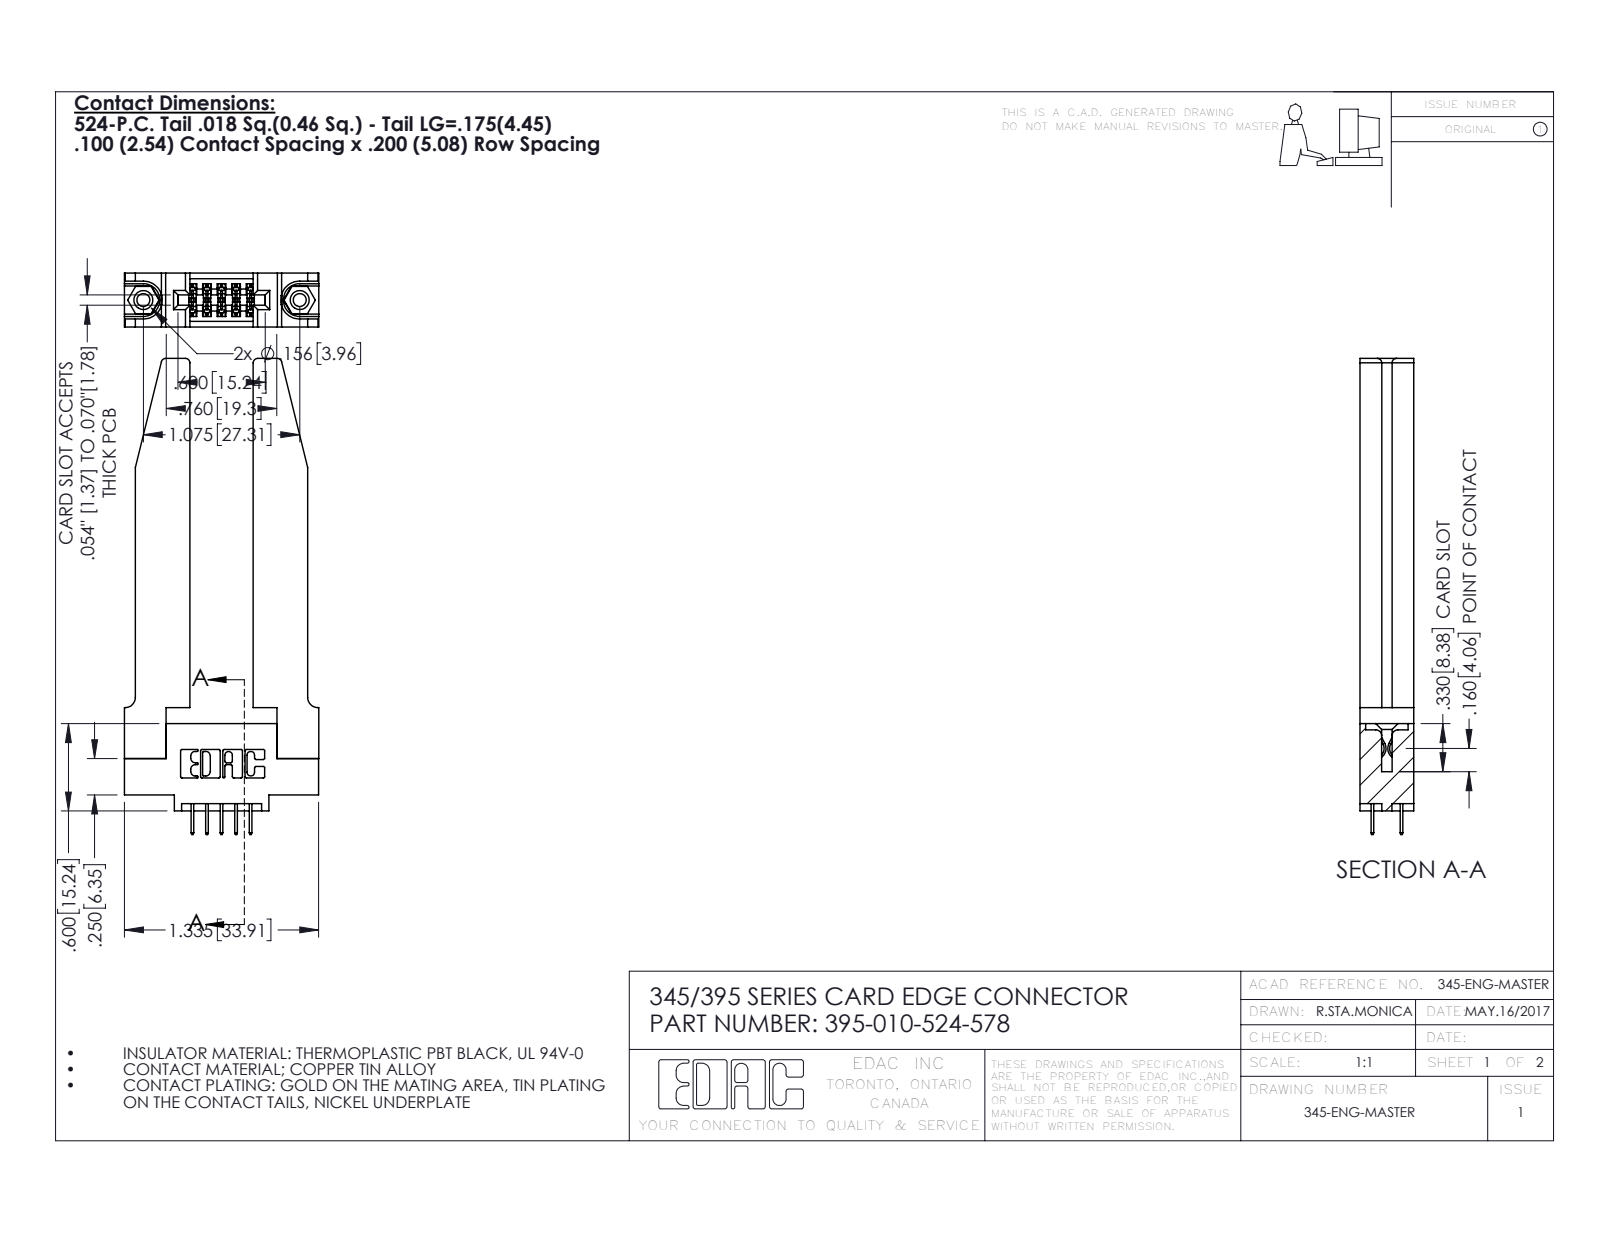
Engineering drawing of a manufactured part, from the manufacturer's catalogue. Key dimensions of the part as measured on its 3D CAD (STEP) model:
Part name (STEP PRODUCT): 345-292-001_345-293-124; 345-250-001_345-250-001-102; 345-220-078_345-220-078; 345 Part_0.110 Offset - 0.156 Dia-TH (+1 more)
STEP written by: SolidWorks 2016 (CONFIG_CONTROL_DESIGN)
Units: inches
Bodies: 15 solids, 904 faces (616 planar, 236 cylindrical, 52 other)
Overall size (bounding box): 3.272 × 1.336 × 0.37
Volume: 0.649 in³ · Surface area: 16.13 in²
Round holes (diameter × count): ⌀0.089 ×2, ⌀0.125 ×2, ⌀0.156 ×2, ⌀0.064 ×1
Round bosses / shafts (diameter × count): ⌀0.155 ×2
Partial cylindrical surfaces — rounded edges, fillets, slot ends (radius × count): R0.01 ×22, R0.006 ×15, R0.03 ×8, R0.007 ×6, R0.031 ×6, R0.026 ×3, R0.014 ×2, R0.019 ×2
Main face-to-face distances: 0.37, 0.15, 0.22, 0.435, 0.072, 0.148, 0.298, 0.077, 0.071, 0.055
Hole centre spacings: 0.27, 0.847, 1.075
